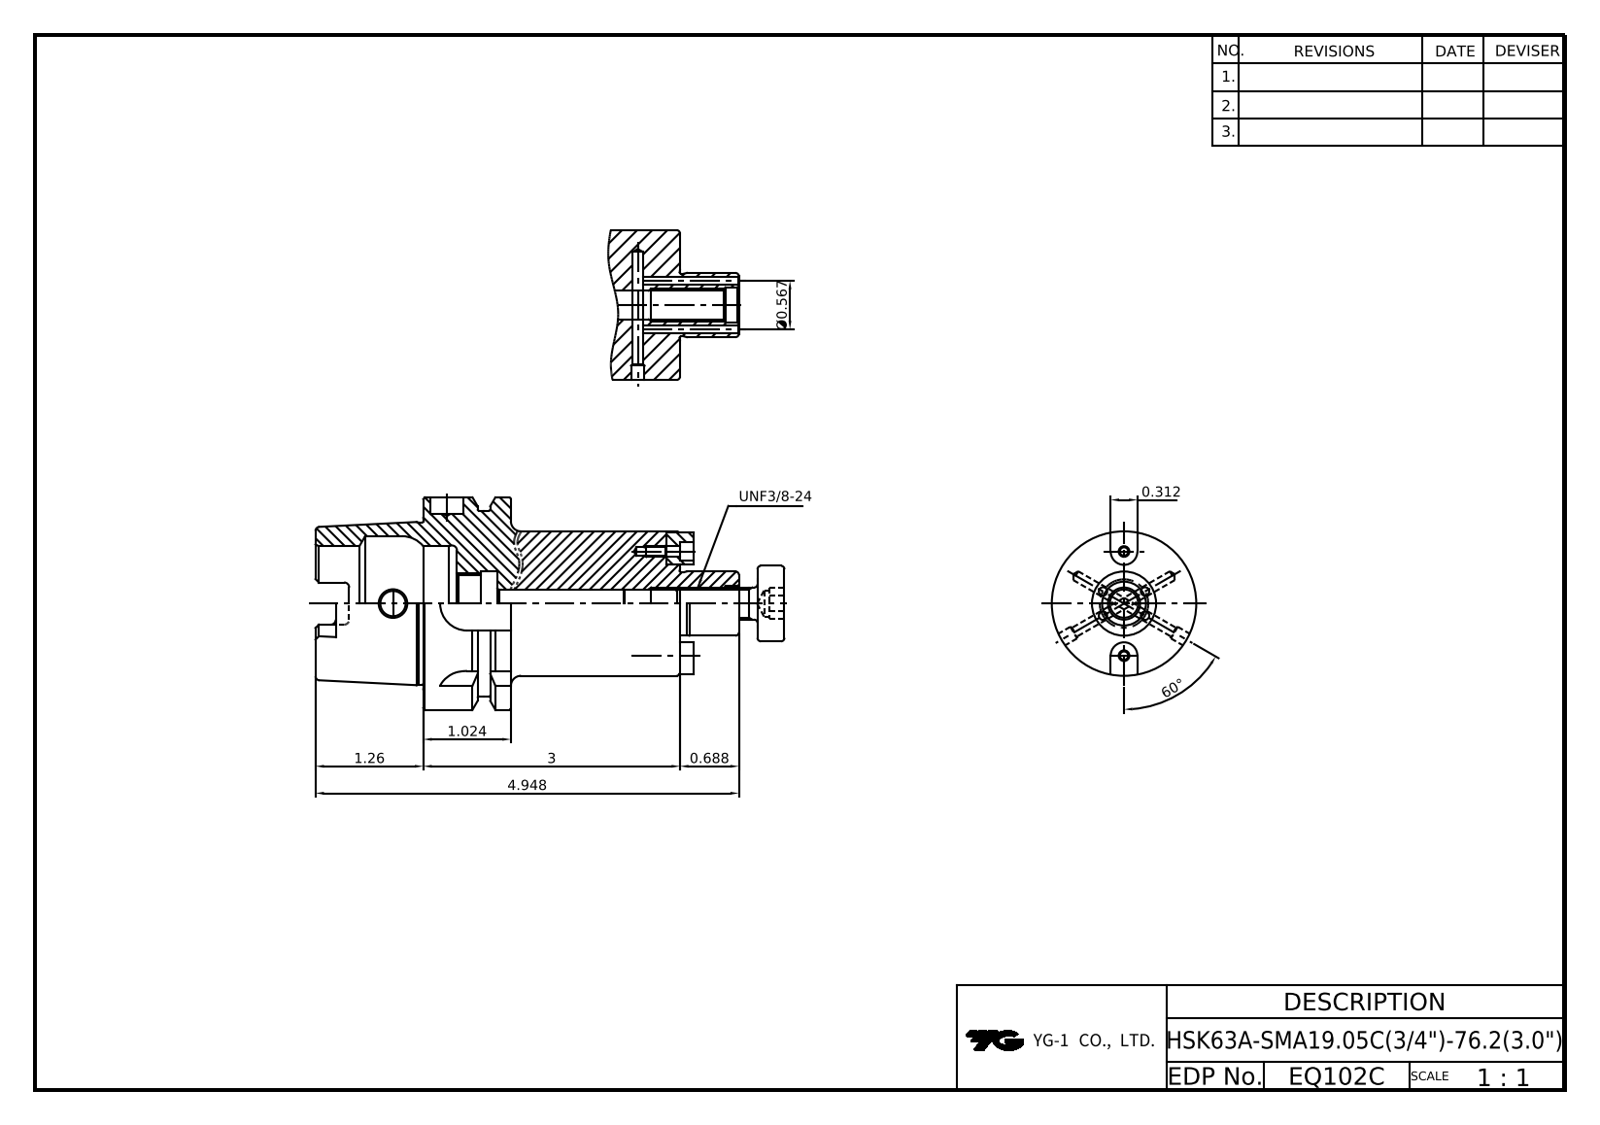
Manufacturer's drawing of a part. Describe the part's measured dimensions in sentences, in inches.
The part is named "LO-HSK63A-SMA19.05C-76.2; COLLAR BOLT-UNF3_8-24x24L; DRIVE KEY-7.93x7.93x9.5; HEX'' WRENCH BOLT-UNC#5-40x5_16L". Its 3-D file was written by "Autodesk Inventor 2025 (AP242_MANAGED_MODEL_BASED_3D_ENGINEERING_MIM_LF)". It is 6 solids with 213 faces: 93 planar, 56 cylindrical and 64 other. Overall it measures 5.657 by 2.48 by 2.48 inches. Its volume is 10.08 cubic inches and its surface area 56.63 square inches. Round holes: 4 of diameter 0.098, 2 of diameter 0.098, 2 of diameter 0.13, 2 of diameter 0.213, 2 of diameter 0.394, 1 of diameter 0.295, 1 of diameter 0.313, 1 of diameter 0.315, 1 of diameter 0.33, 1 of diameter 0.666, 1 of diameter 0.748, 1 of diameter 1.339. Round bosses or shafts: 2 of diameter 0.205, 2 of diameter 0.125, 1 of diameter 2.48, 1 of diameter 2.165, 1 of diameter 1.891, 1 of diameter 1.75, 1 of diameter 0.882, 1 of diameter 0.75. Partial cylindrical surfaces (rounded edges, fillets, slot ends): 6 of radius 0.059, 4 of radius 0.113, 4 of radius 0.156, 4 of radius 0.315. The main face-to-face distances are 3, 1.024, 1.976, 0.394, 0.63, 2.606, 1.26, 0.157, 1.654, 2.283. The hole center spacings are 0.283, 0.537, 0.799, 0.491, 0.567, 0.619, 1.238.
